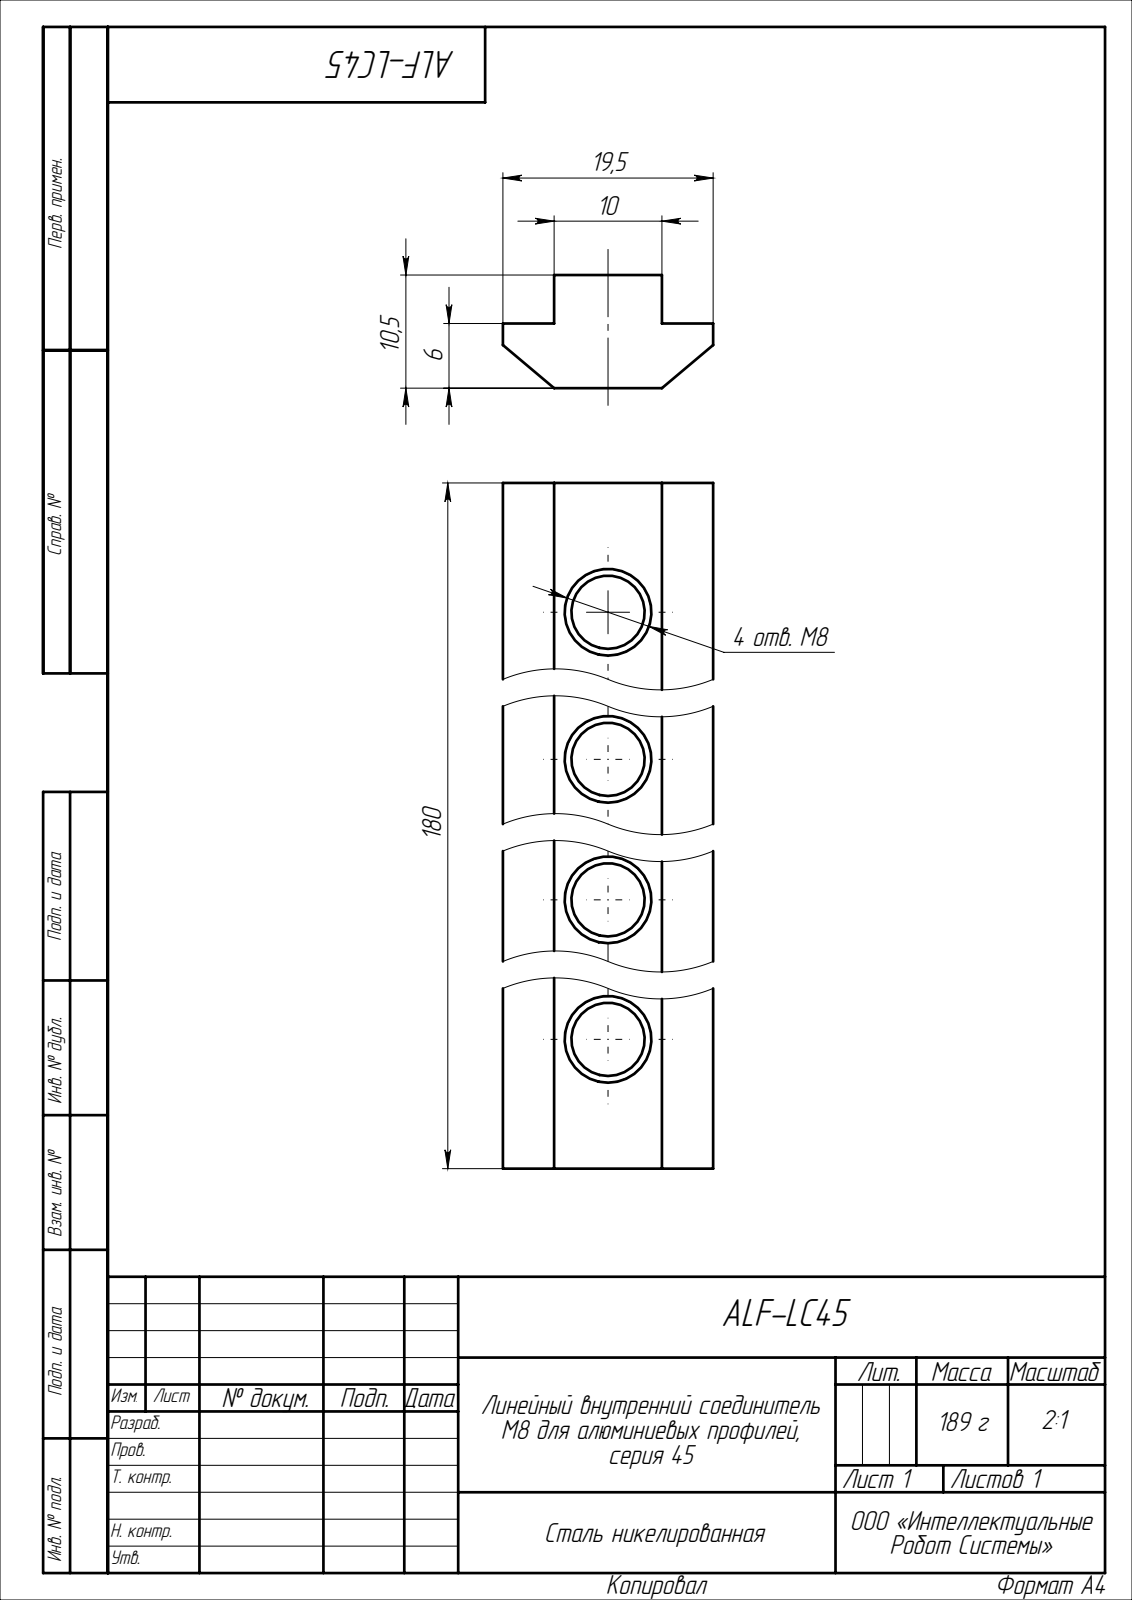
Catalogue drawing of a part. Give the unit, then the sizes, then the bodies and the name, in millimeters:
Units: millimetres
Overall size (bounding box): 180 × 19.5 × 10.5
Round holes (diameter × count): ⌀6.8 ×4
Main face-to-face distances: 6, 10.5, 4.5, 10, 4.75, 14.75, 19.5, 180
Hole centre spacings: 63, 93, 30, 156
Volume: 24 179 mm³ · Surface area: 10 720 mm²
Bodies: 1 solid, 36 faces (12 planar, 8 cylindrical, 16 other)
Part name (STEP PRODUCT): ALF-LC45
STEP written by: SolidWorks 2022 (CONFIG_CONTROL_DESIGN)
